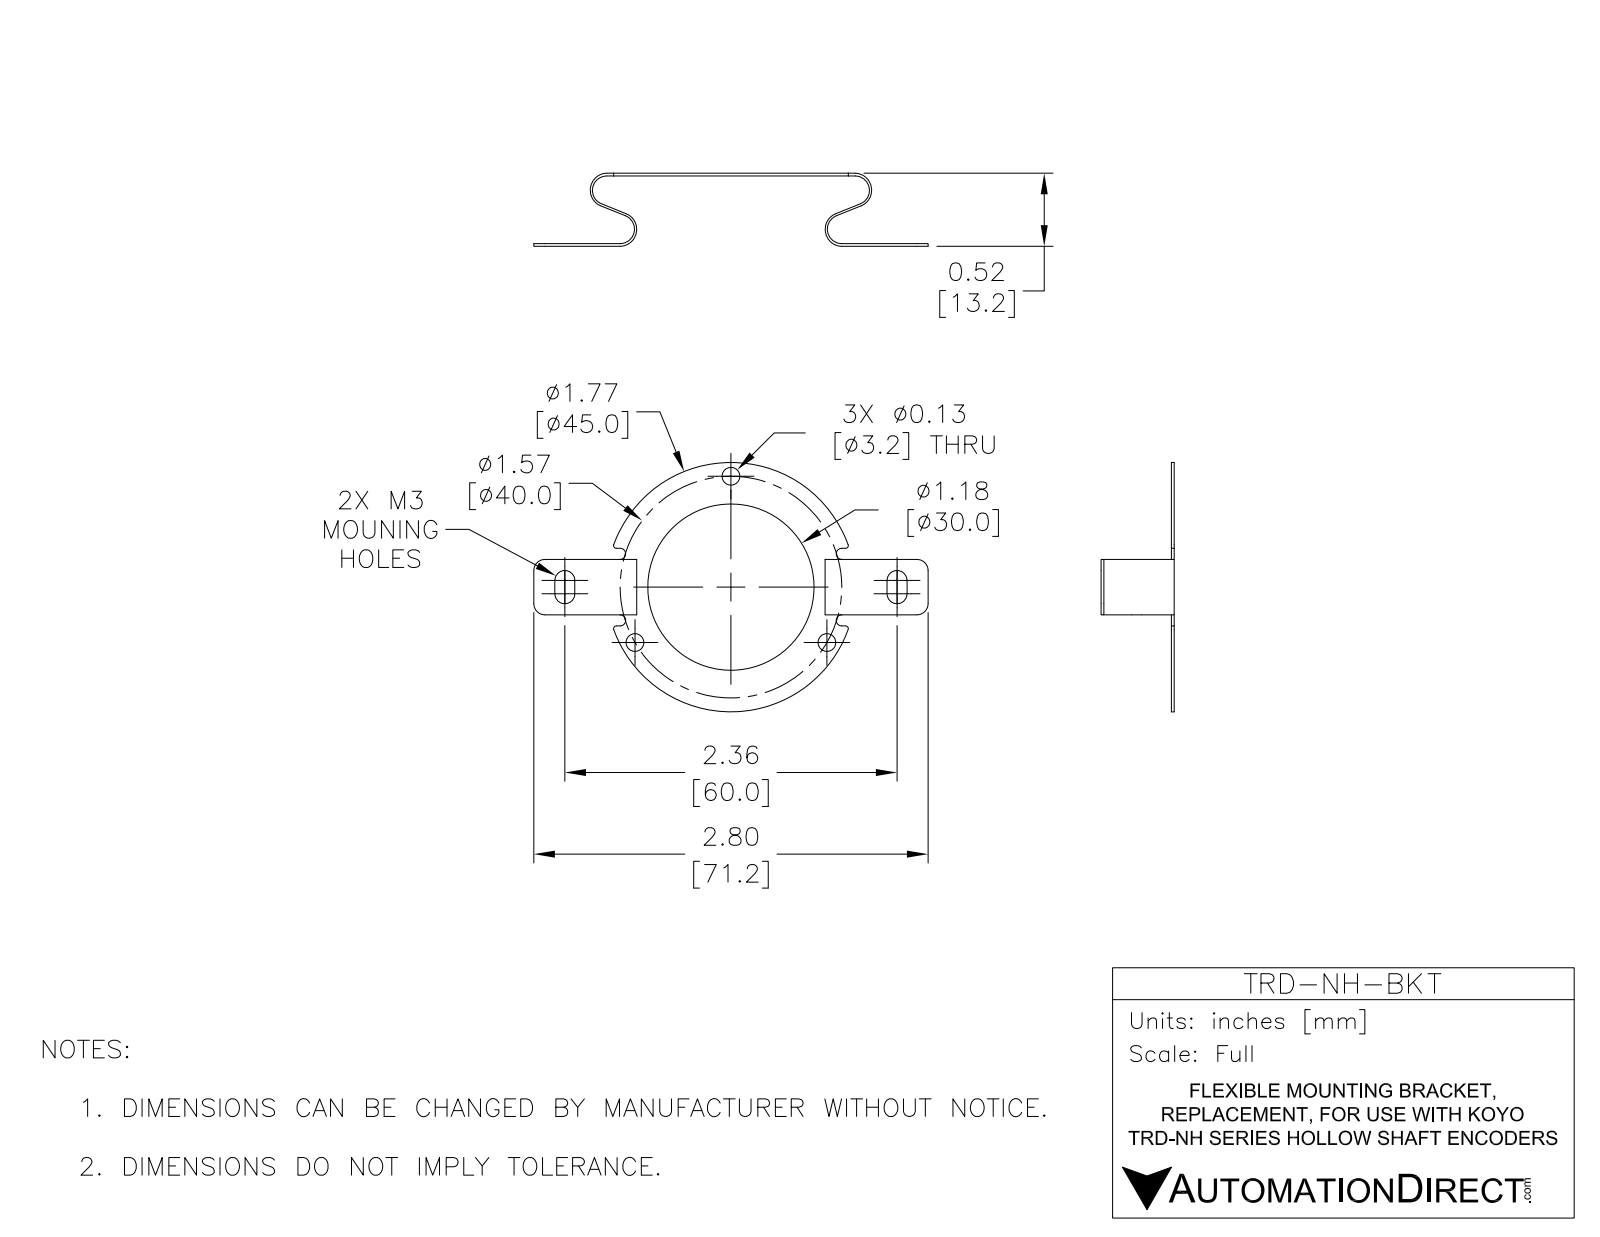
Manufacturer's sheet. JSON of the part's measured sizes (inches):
{"part_name": "TRD-NH-BKT", "step_written_by": "SolidWorks 2016 (AUTOMOTIVE_DESIGN)", "units": "inches", "bodies": {"solids": 1, "faces": 73, "planar": 32, "cylindrical": 41, "other": 0}, "overall_size": [2.801, 1.772, 0.512], "volume_in3": 0.037, "surface_area_in2": 4.986, "round_holes": [[0.126, 3], [1.181, 1]], "partial_cylinders_radius": [[0.02, 4], [0.039, 4], [0.071, 4], [0.079, 4], [0.102, 4], [0.118, 4], [0.886, 1], [1.11, 1]], "face_to_face_distances": [0.016, 0.496, 0.48, 0.512, 0.394, 2.801, 0.079, 0.472, 0.551], "hole_center_spacings": [0.787, 1.364]}
